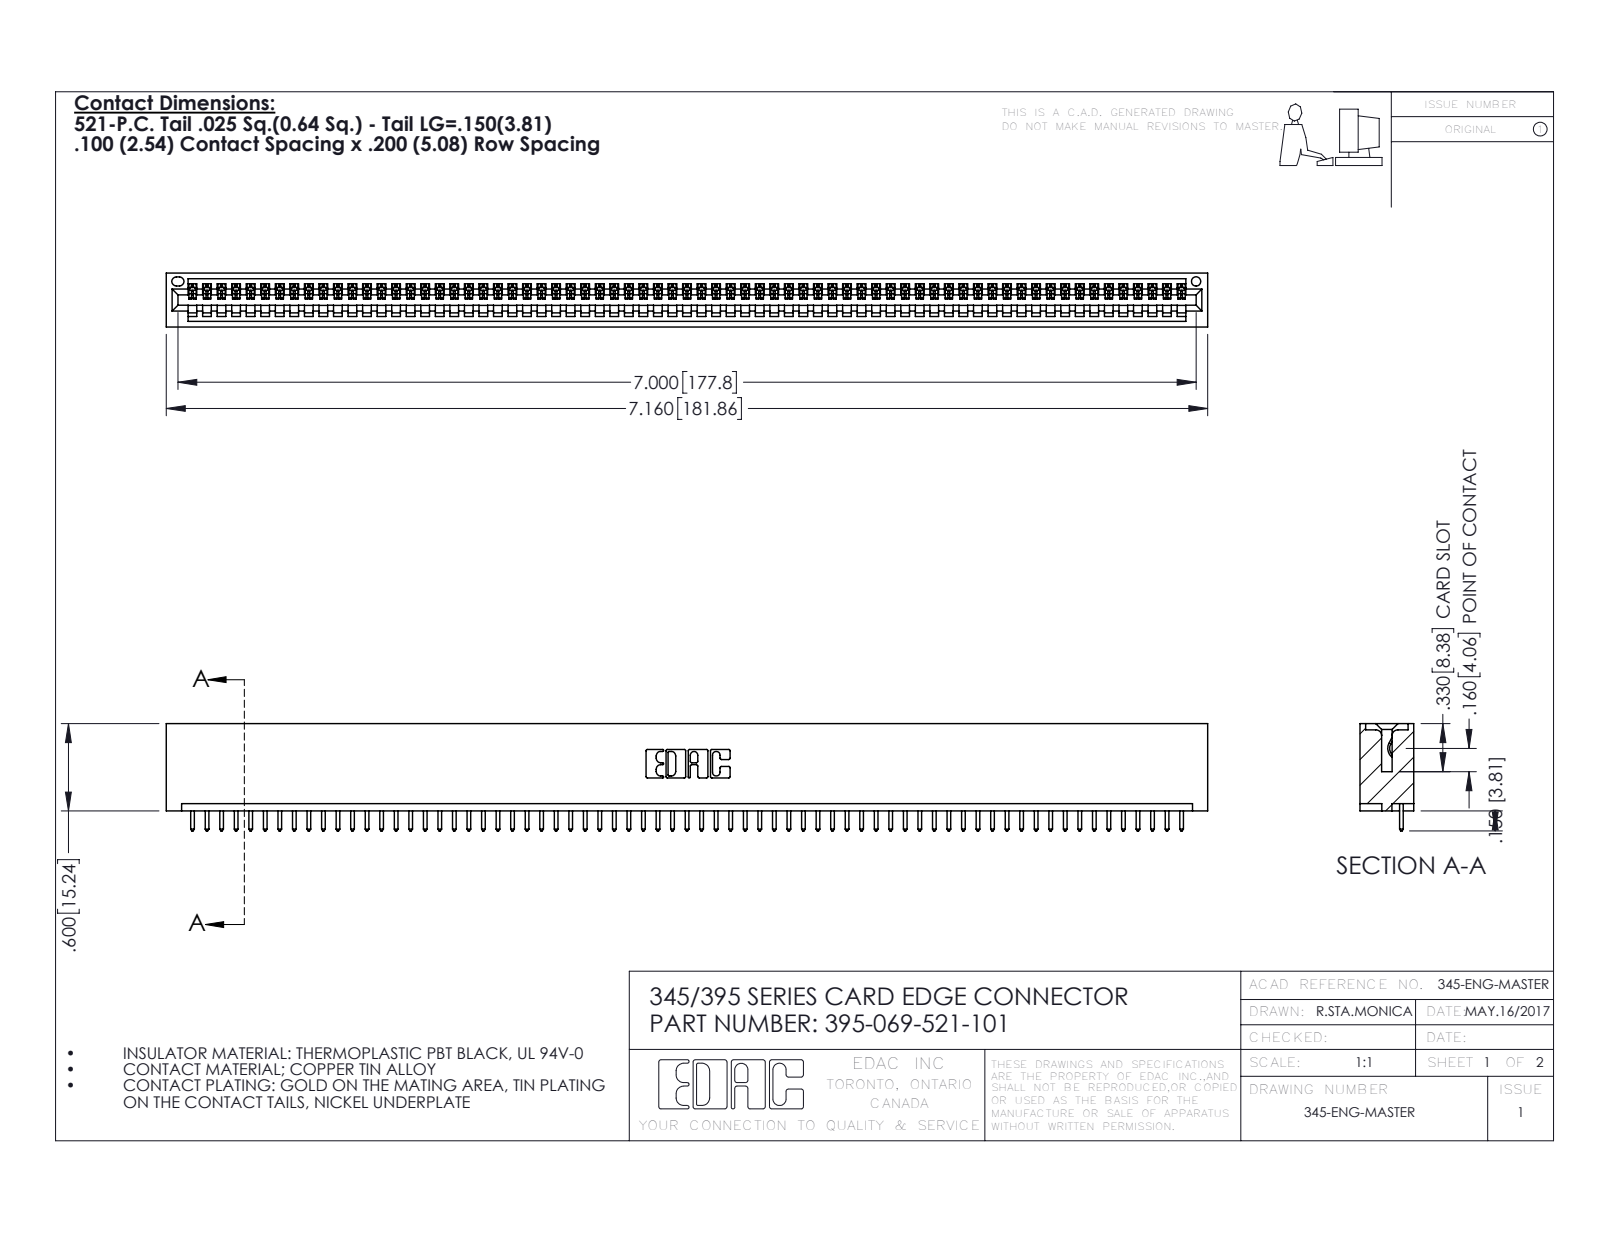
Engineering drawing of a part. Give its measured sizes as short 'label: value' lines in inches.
name: 395-069-521-101; 345 Part_No Mounting Lugs; 345-292-001_345-293-121
written by: SolidWorks 2016 (CONFIG_CONTROL_DESIGN)
unit: in
bodies: 70 solids, 4120 faces (2836 planar, 1284 cylindrical, 0 other)
size: 7.16 × 0.737 × 0.37
volume: 1.091 in³; area: 36.51 in²
holes: 1× ⌀0.064
rounds: 138× R0.006, 138× R0.01, 22× R0.01, 6× R0.007, 6× R0.031, 3× R0.026, 2× R0.031, 2× R0.04
face distances: 0.298, 0.072, 0.37, 0.2, 0.098, 0.272, 0.025, 0.225, 0.149, 0.072
